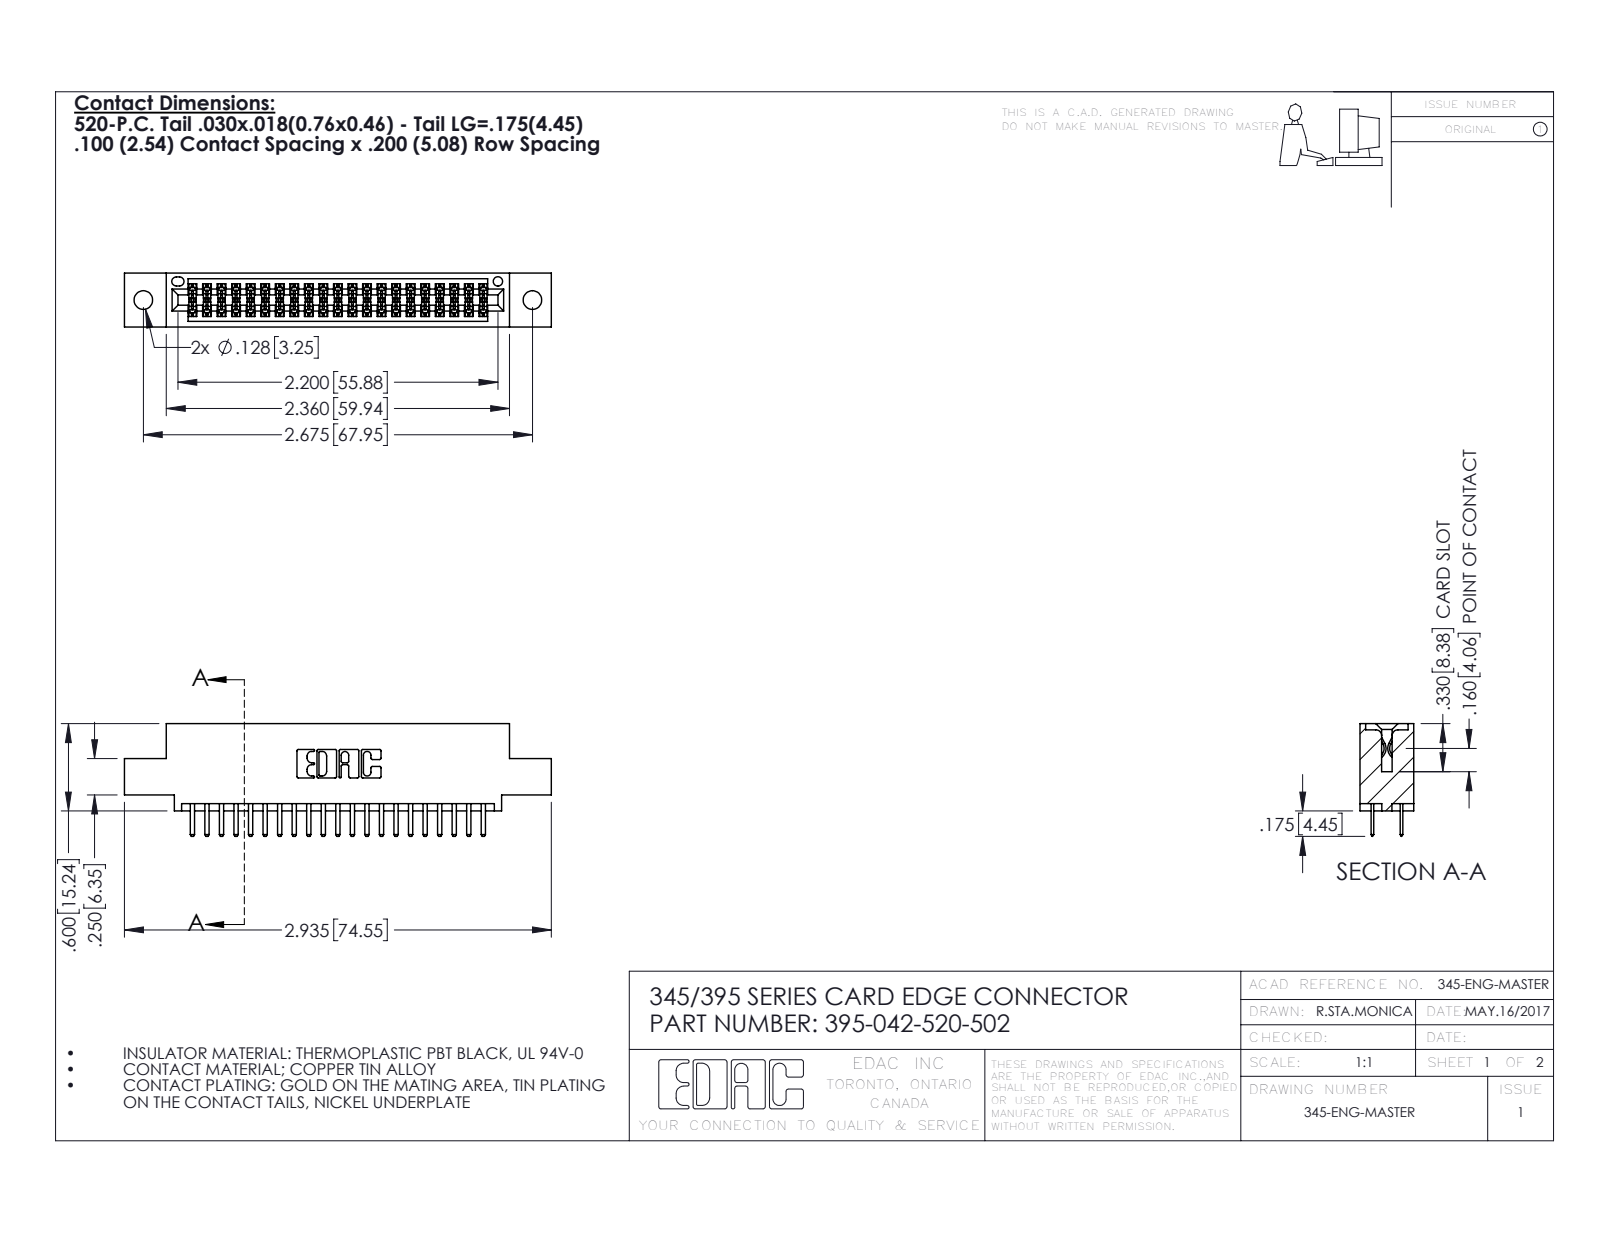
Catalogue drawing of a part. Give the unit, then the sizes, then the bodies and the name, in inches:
Units: inches
Overall size (bounding box): 2.935 × 0.775 × 0.37
Round holes (diameter × count): ⌀0.128 ×2, ⌀0.064 ×1
Partial cylindrical surfaces — rounded edges, fillets, slot ends (radius × count): R0.006 ×63, R0.01 ×46, R0.01 ×22, R0.007 ×6, R0.031 ×6, R0.026 ×3, R0.014 ×2, R0.019 ×2
Main face-to-face distances: 0.298, 0.072, 0.2, 0.37, 0.098, 0.272, 0.025, 0.225, 0.022, 0.072
Hole centre spacings: 0.27, 2.441, 2.675
Volume: 0.422 in³ · Surface area: 14.88 in²
Bodies: 43 solids, 2398 faces (1554 planar, 844 cylindrical, 0 other)
Part name (STEP PRODUCT): 395-042-520-502; 345-292-001_345-293-120; 345 Part_0.110 Offset - 0.128 Dia
STEP written by: SolidWorks 2016 (CONFIG_CONTROL_DESIGN)
